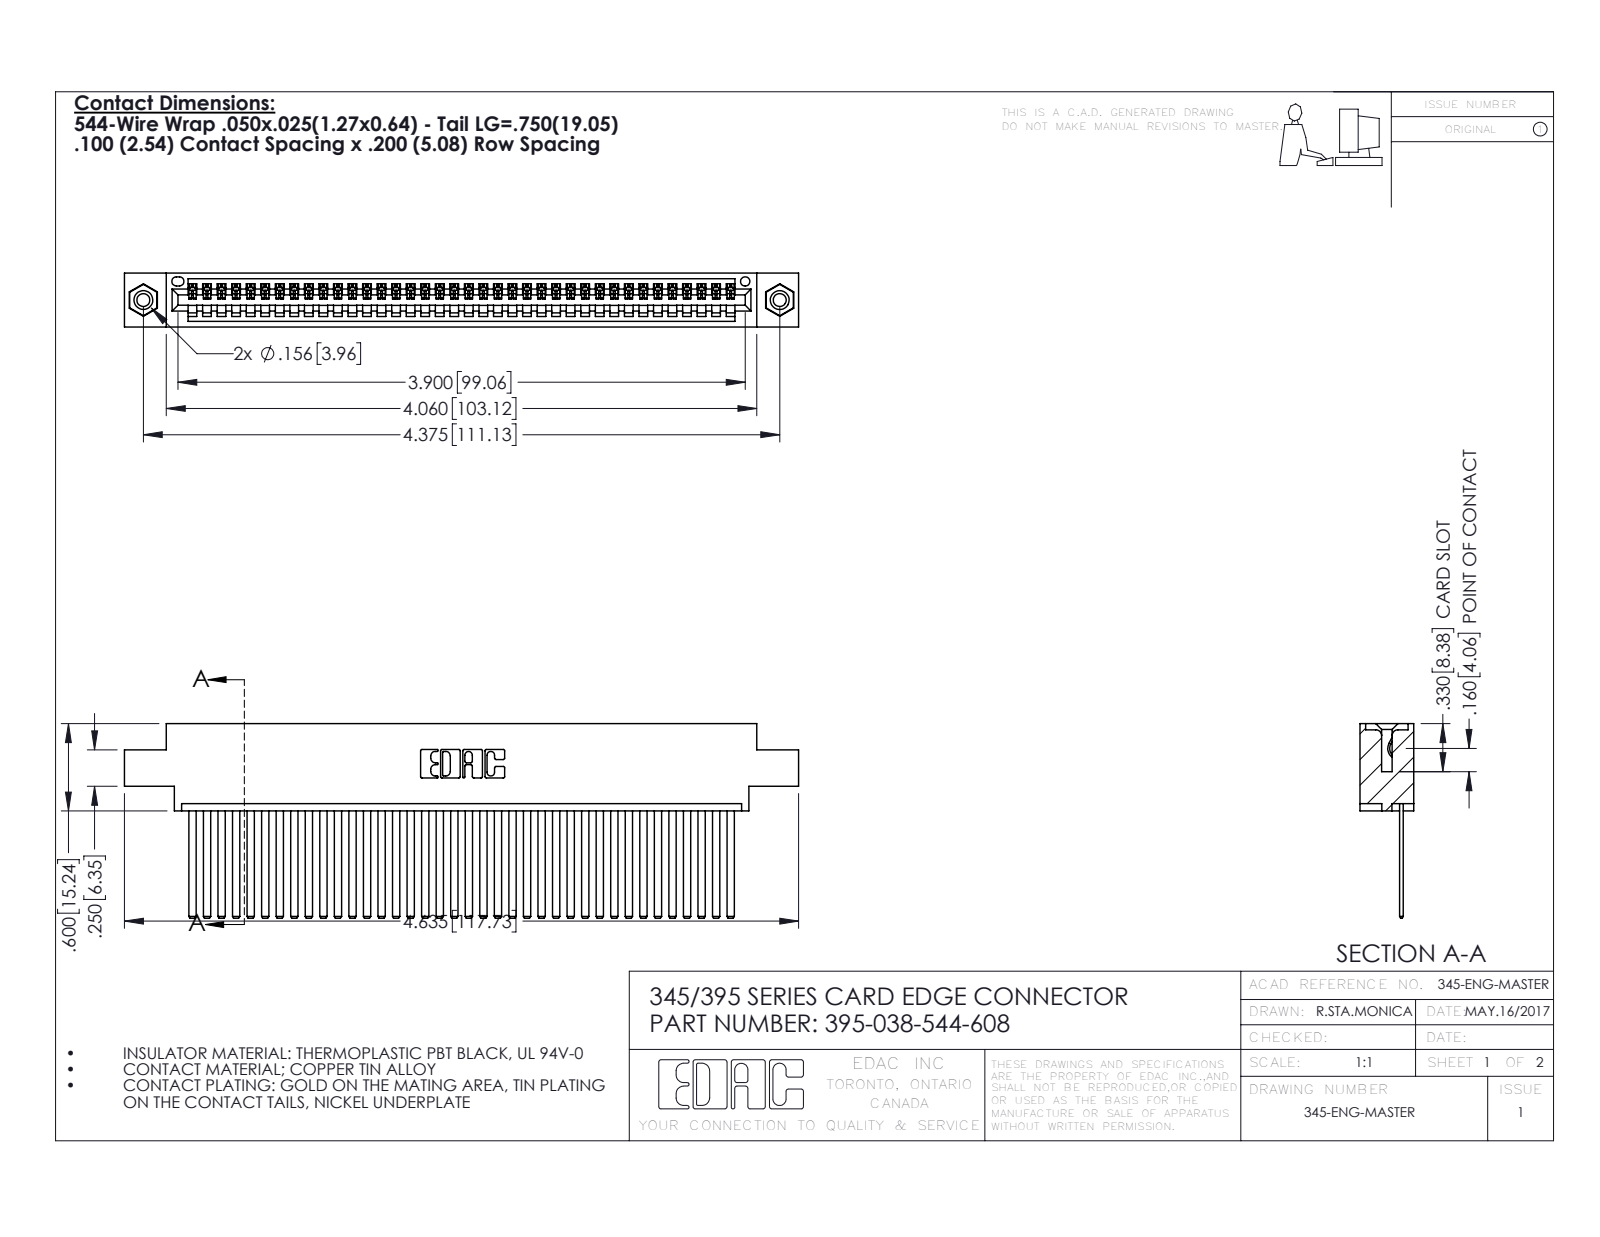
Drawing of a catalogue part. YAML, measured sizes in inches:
part_name: "345 Part_0.170 Offset - 0.156 Dia-TI; 395-038-544-608; 345-250-001_345-250-003-102; 345-292-001_345-293-144"
step_written_by: "SolidWorks 2016 (CONFIG_CONTROL_DESIGN)"
units: inches
bodies: {solids: 41, faces: 2166, planar: 1484, cylindrical: 666, other: 16}
overall_size: [4.635, 1.337, 0.37]
volume: 0.7
surface_area: 25.81
round_holes:
  - {diameter: 0.089, count: 2}
  - {diameter: 0.125, count: 2}
  - {diameter: 0.156, count: 2}
  - {diameter: 0.064, count: 1}
round_bosses_or_shafts:
  - {diameter: 0.155, count: 2}
partial_cylinders:
  - {radius: 0.006, count: 76}
  - {radius: 0.01, count: 22}
  - {radius: 0.007, count: 6}
  - {radius: 0.031, count: 6}
  - {radius: 0.026, count: 3}
  - {radius: 0.031, count: 2}
  - {radius: 0.04, count: 2}
  - {radius: 0.014, count: 1}
face_to_face_distances: [0.072, 0.298, 0.025, 0.098, 0.272, 0.37, 0.2, 0.225, 0.175, 0.149]
hole_center_spacings: [0.27, 4.139, 4.375]
